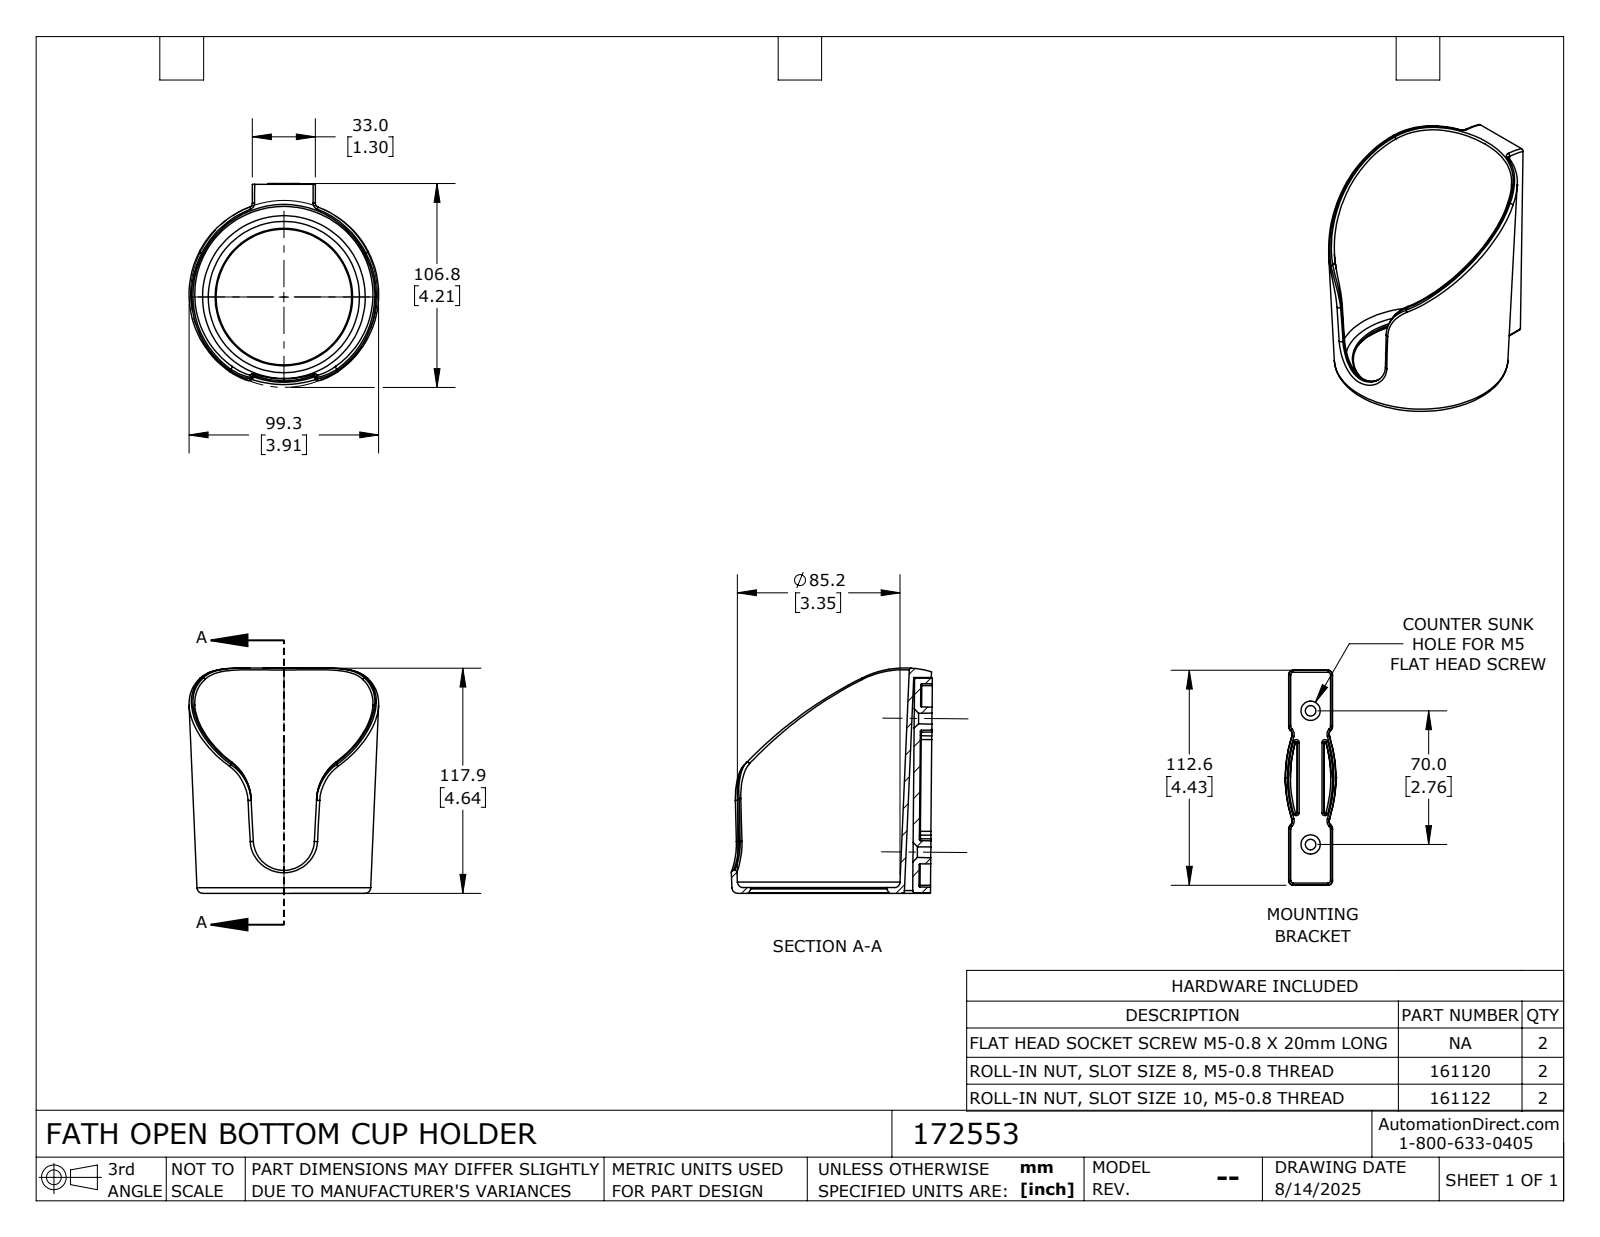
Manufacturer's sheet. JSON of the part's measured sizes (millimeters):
{"part_name": "172553", "step_written_by": "SolidWorks 2024 (CONFIG_CONTROL_DESIGN)", "units": "millimeters", "bodies": {"solids": 2, "faces": 290, "planar": 58, "cylindrical": 47, "other": 185}, "overall_size": [119.98, 105.3, 99.32], "volume_mm3": 111158, "surface_area_mm2": 71981, "partial_cylinders_radius": [[0.5, 8], [1, 8], [1.5, 6], [3, 4], [2, 2], [10, 2], [67.8, 2], [70.5, 2]], "face_to_face_distances": [3, 8.81, 27.75, 24.75, 0.5, 9.31, 1.5, 12.38, 6.31, 5.81]}
